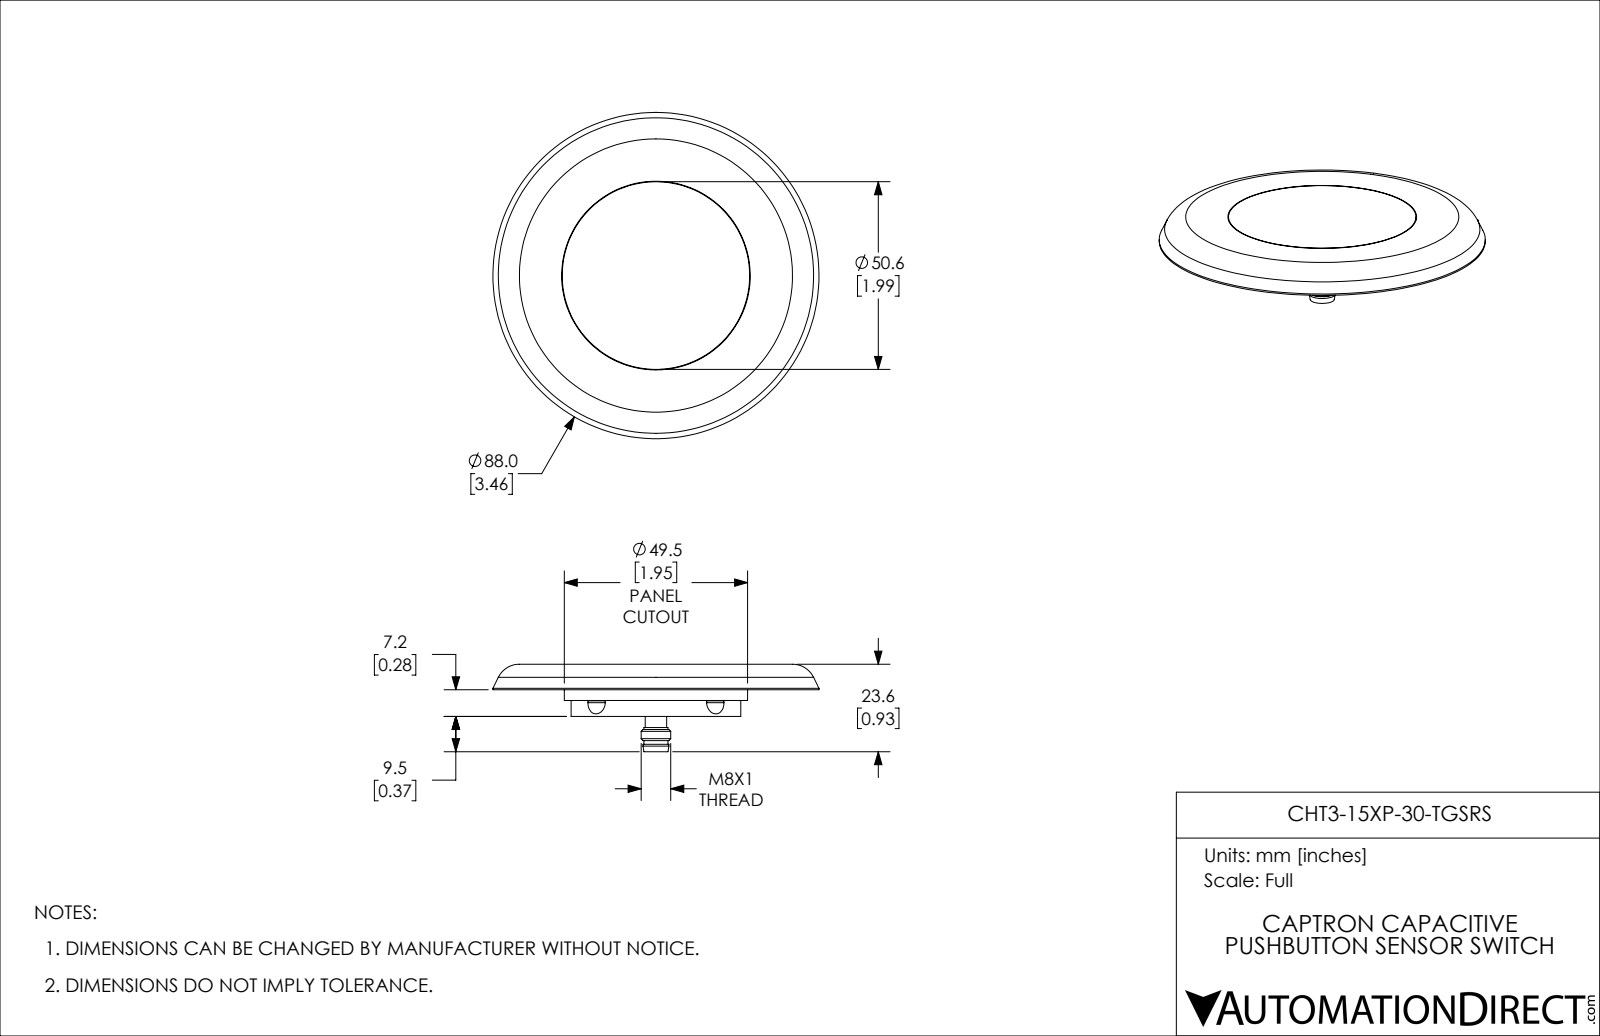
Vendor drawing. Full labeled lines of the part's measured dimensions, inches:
Part name (STEP PRODUCT): CHT3-15XP-30-TGSRS
STEP written by: SolidWorks 2019 (CONFIG_CONTROL_DESIGN)
Units: inches
Bodies: 9 solids, 87 faces (25 planar, 36 cylindrical, 26 other)
Overall size (bounding box): 3.465 × 3.465 × 0.929
Volume: 3.031 in³ · Surface area: 33.39 in²
Round holes (diameter × count): ⌀0.236 ×1, ⌀1.815 ×1, ⌀2.004 ×1
Round bosses / shafts (diameter × count): ⌀0.039 ×4, ⌀1.992 ×1, ⌀1.948 ×1, ⌀1.803 ×1, ⌀0.315 ×1, ⌀0.276 ×1, ⌀0.256 ×1, ⌀0.228 ×1
Partial cylindrical surfaces — rounded edges, fillets, slot ends (radius × count): R0.197 ×4, R0.035 ×1
Main face-to-face distances: 0.272, 0.181, 0.091, 0.283, 0.465, 0.555, 0.02, 0.295, 0.303, 0.169
